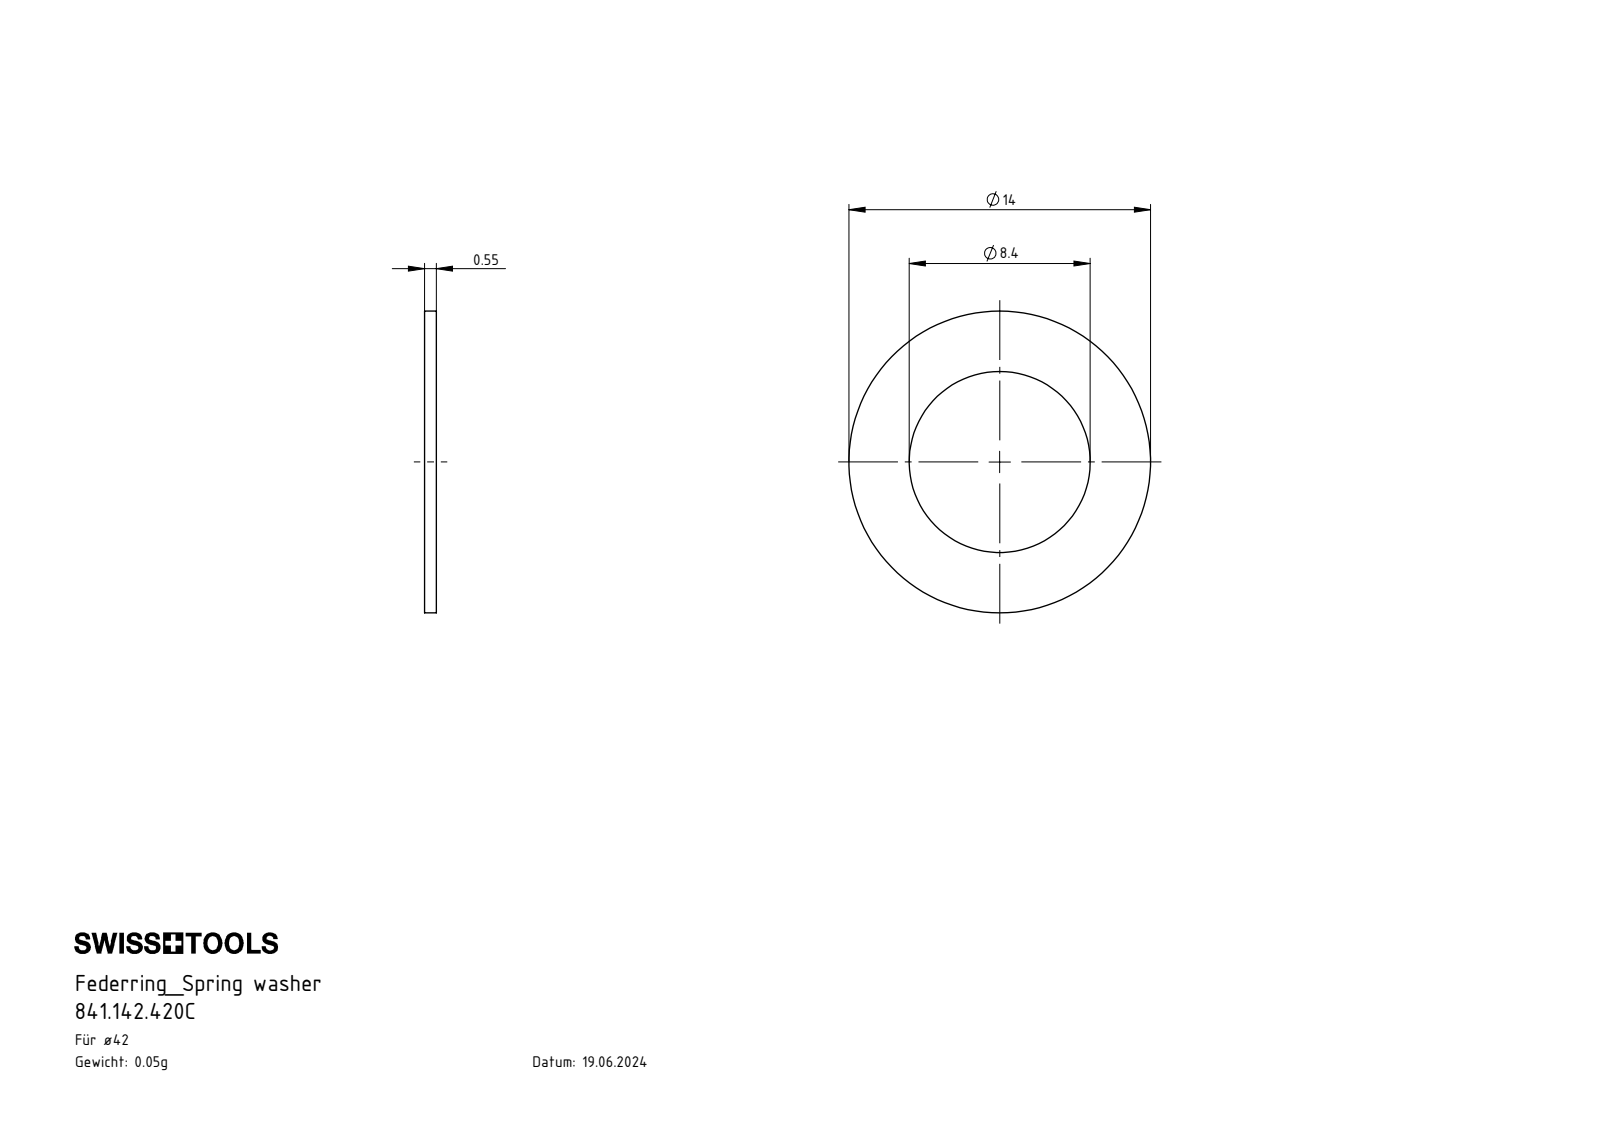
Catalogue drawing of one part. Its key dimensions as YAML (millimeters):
part_name: "841.142.420C"
step_written_by: "SolidWorks 2022 (AUTOMOTIVE_DESIGN)"
units: millimeters
bodies: {solids: 1, faces: 6, planar: 2, cylindrical: 4, other: 0}
overall_size: [14, 14, 0.55]
volume: 54
surface_area: 236
round_holes:
  - {diameter: 8.4, count: 1}
round_bosses_or_shafts:
  - {diameter: 14, count: 1}
face_to_face_distances: [0.55]
